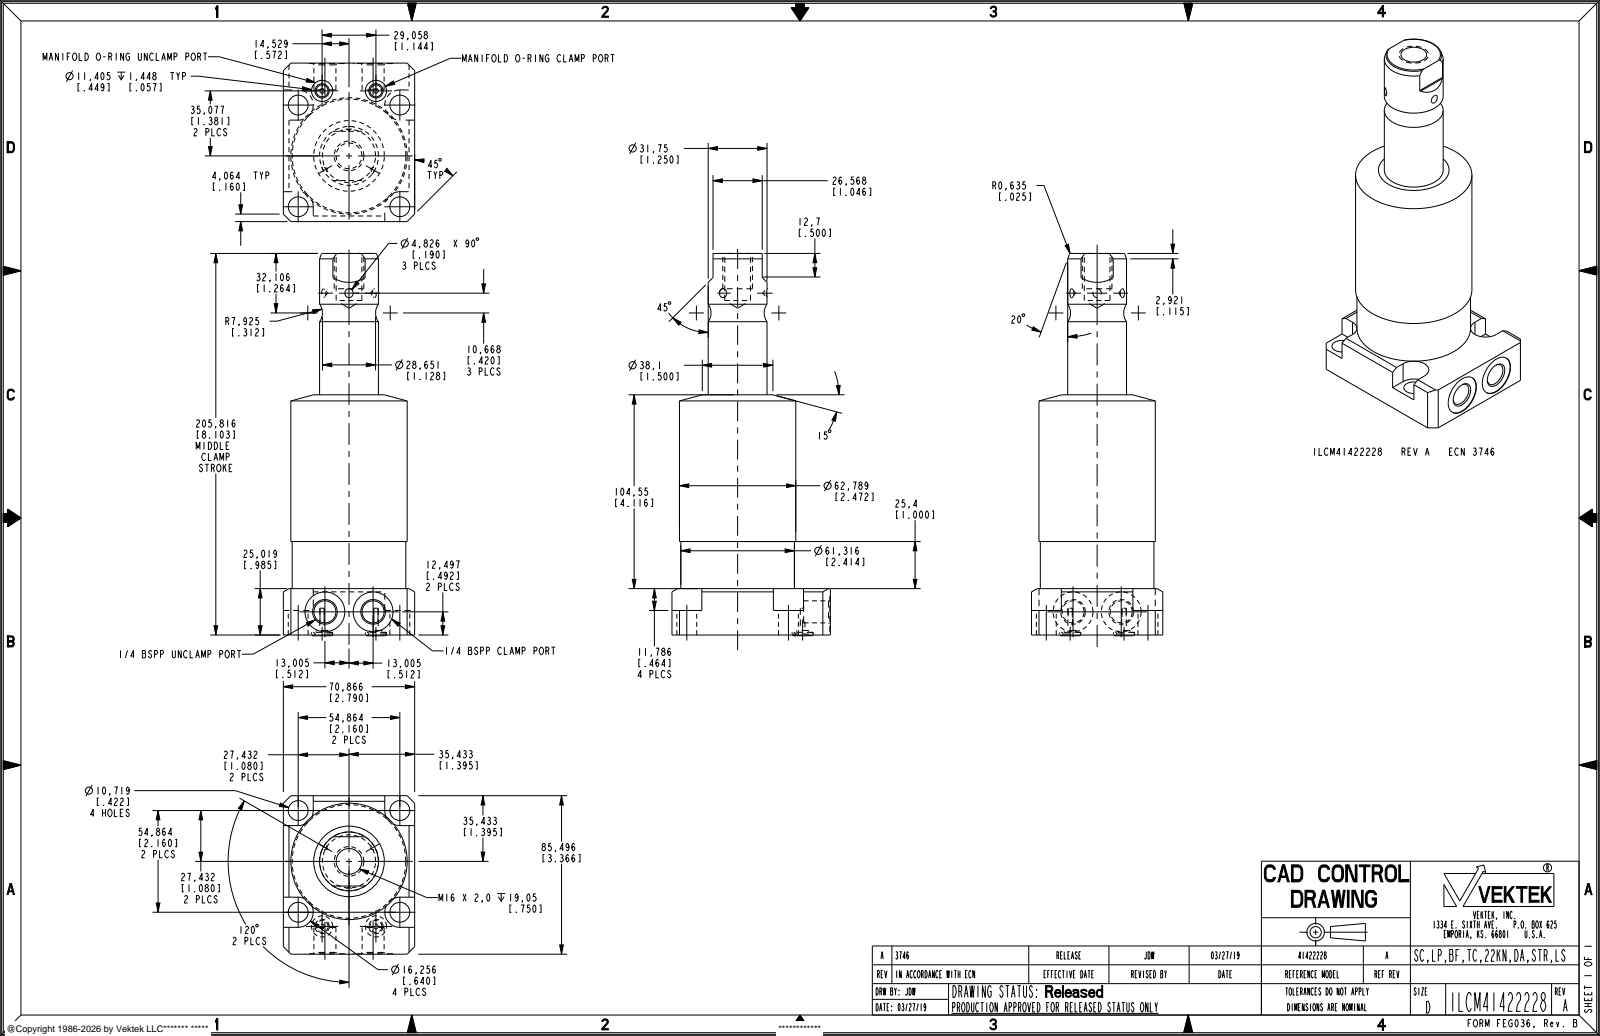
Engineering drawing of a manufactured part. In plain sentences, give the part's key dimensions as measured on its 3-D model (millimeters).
The part is named "ILCM41422228". Its 3-D file was written by "PRO/ENGINEER BY PARAMETRIC TECHNOLOGY CORPORATION, 2013320 (AUTOMOTIVE_DESIGN)". It is 1 solid with 124 faces: 48 planar, 48 cylindrical and 28 other. Overall it measures 206.22 by 85.5 by 70.87 millimeters. Its volume is 501 808 cubic millimeters and its surface area 52 569 square millimeters. Round holes: 4 of diameter 10.72, 2 of diameter 2.49, 2 of diameter 6.5, 2 of diameter 11.4, 2 of diameter 11.89, 2 of diameter 21.49, 1 of diameter 13.87. Round bosses or shafts: 1 of diameter 62.79, 1 of diameter 61.32, 1 of diameter 31.75, 1 of diameter 16. Partial cylindrical surfaces (rounded edges, fillets, slot ends): 4 of radius 8.13, 2 of radius 0.76. The main face-to-face distances are 25.02, 70.86, 85.49, 11.79, 13.23, 180.8, 192.59, 205.82, 85.24, 54.73. The hole center spacings are 38.79, 54.86, 15, 37.97, 42.65, 63.83, 75.29, 77.58.
